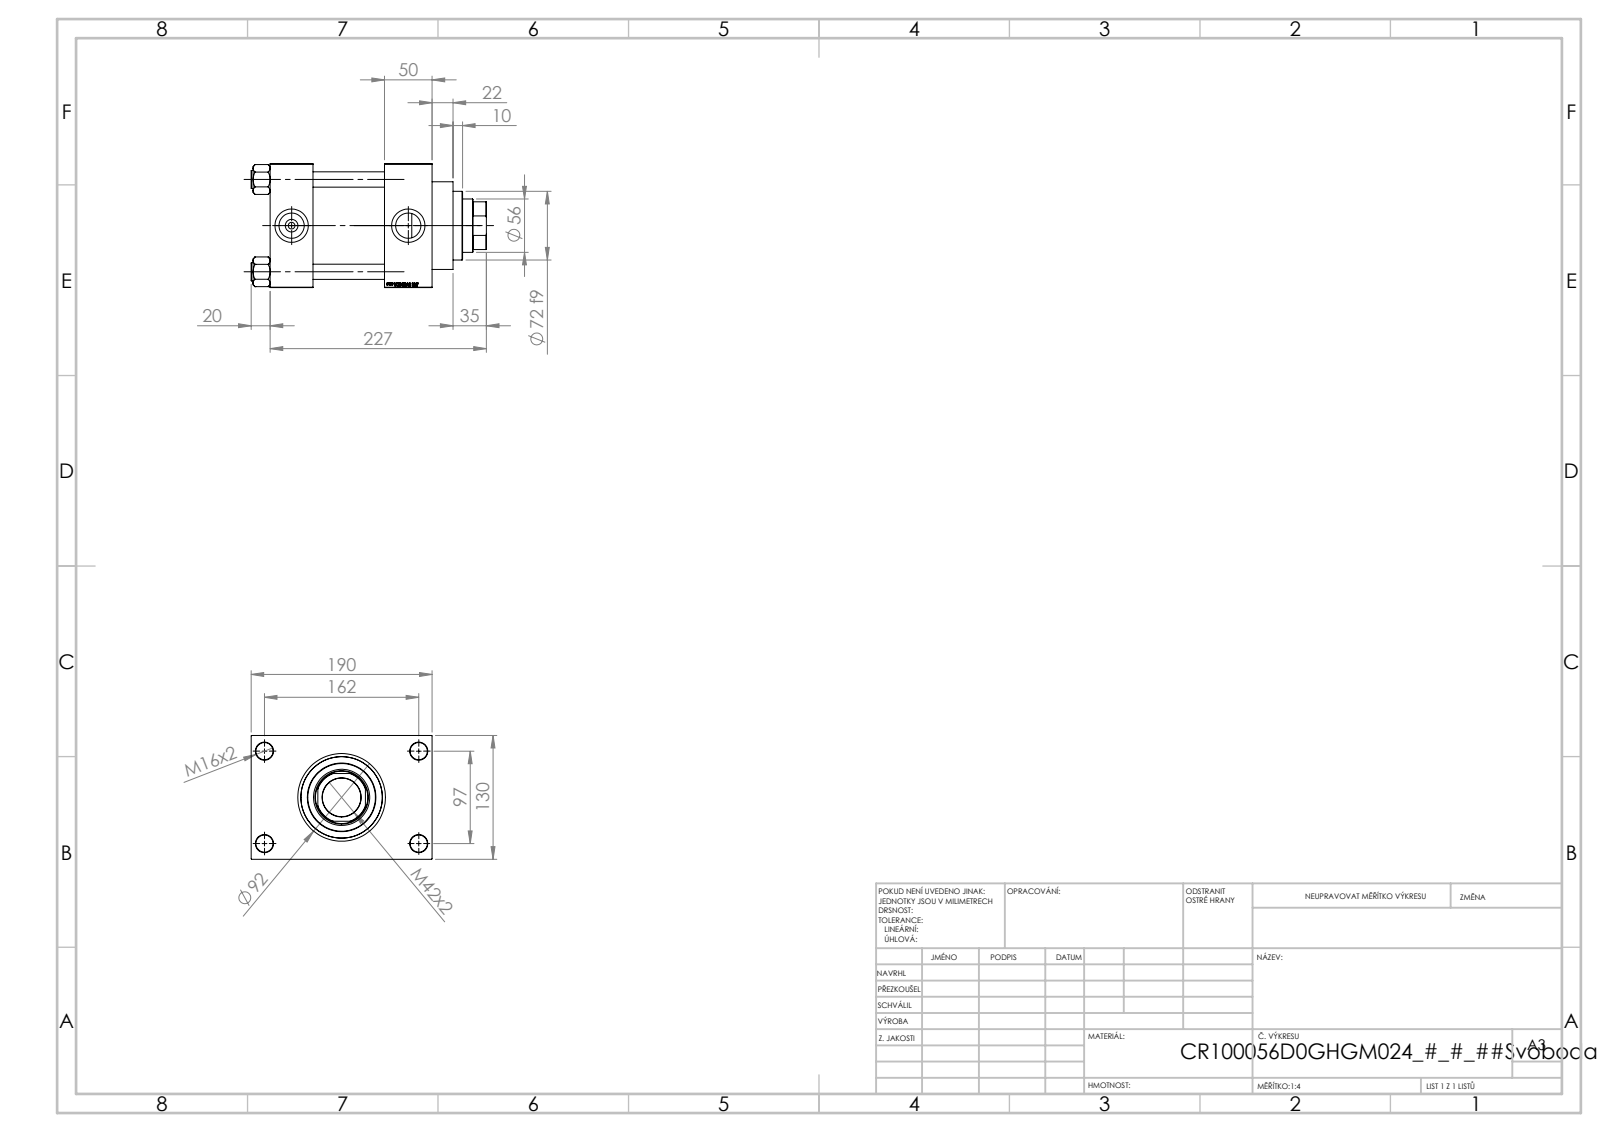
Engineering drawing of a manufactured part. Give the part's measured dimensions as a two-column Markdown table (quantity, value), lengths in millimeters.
| quantity | value |
| --- | --- |
| part name | V215CR_VCP_D; NUT_M5_D; V215CR_D_Body; V215CR_D_TYCINKA (+1 more) |
| STEP written by | SolidWorks 2019 (CONFIG_CONTROL_DESIGN) |
| units | millimeters |
| bodies | 11 solids, 1151 faces (545 planar, 88 cylindrical, 518 other) |
| overall size | 247 × 190 × 130 |
| volume | 2 645 000 mm³ |
| surface area | 366 460 mm² |
| round holes (diameter × count) | 16 × 4, 18 × 4, 7 × 2, 26.44 × 2, 35 × 2, 40.5 × 1, 56 × 1, 59 × 1, 76 × 1, 85.5 × 1, 100 × 1 |
| round bosses / shafts (diameter × count) | 19 × 4, 106 × 1, 92 × 1, 72 × 1 |
| partial cylindrical surfaces (radius × count) | 27 × 1 |
| main face-to-face distances | 130, 120, 50, 45, 75, 125, 170, 30, 160, 96 |
| hole center spacings | 32.55, 68.52, 94.41, 96.9, 102.27, 129.45, 161.73, 97 |
